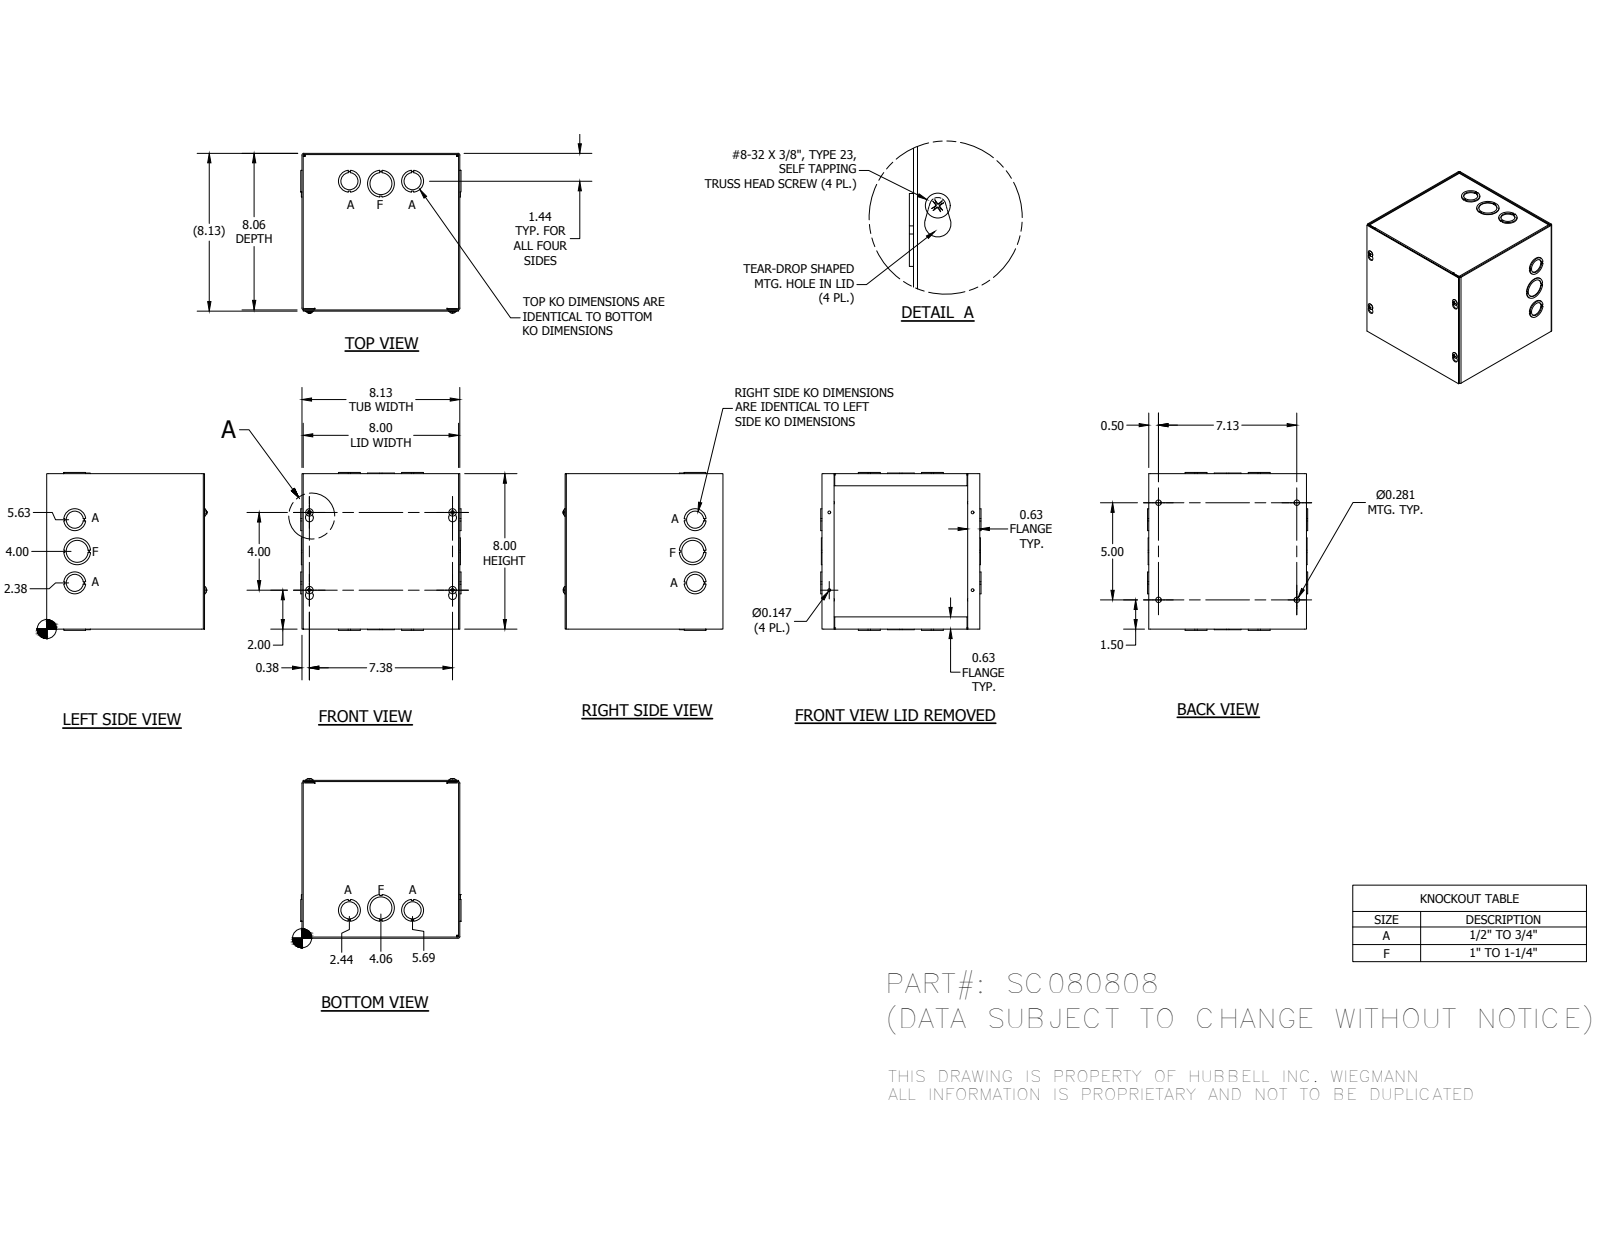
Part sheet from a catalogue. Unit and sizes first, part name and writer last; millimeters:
Units: millimetres
Overall size (bounding box): 209.55 × 208.92 × 206.38
Round holes (diameter × count): ⌀28.57 ×7, ⌀22.22 ×5, ⌀3.73 ×4, ⌀7.14 ×4, ⌀34.92 ×2
Round bosses / shafts (diameter × count): ⌀9.75 ×4, ⌀4.17 ×4
Partial cylindrical surfaces — rounded edges, fillets, slot ends (radius × count): R0.79 ×12, R2.38 ×12, R3.17 ×4, R5.16 ×4
Main face-to-face distances: 1.59, 204.79, 203.2, 201.61, 206.38, 200.02, 3.18, 1.58, 201.62, 3.17
Hole centre spacings: 13.09, 41.4, 114.34, 184.59, 216.74, 82.56, 101.6, 127
Bodies: 23 solids, 605 faces (417 planar, 120 cylindrical, 68 other)
Part name (STEP PRODUCT): SC080808BLR; SC0808TB; SC0808LPA; 34056 (+1 more)
STEP written by: Autodesk Inventor 2014 (AUTOMOTIVE_DESIGN)
